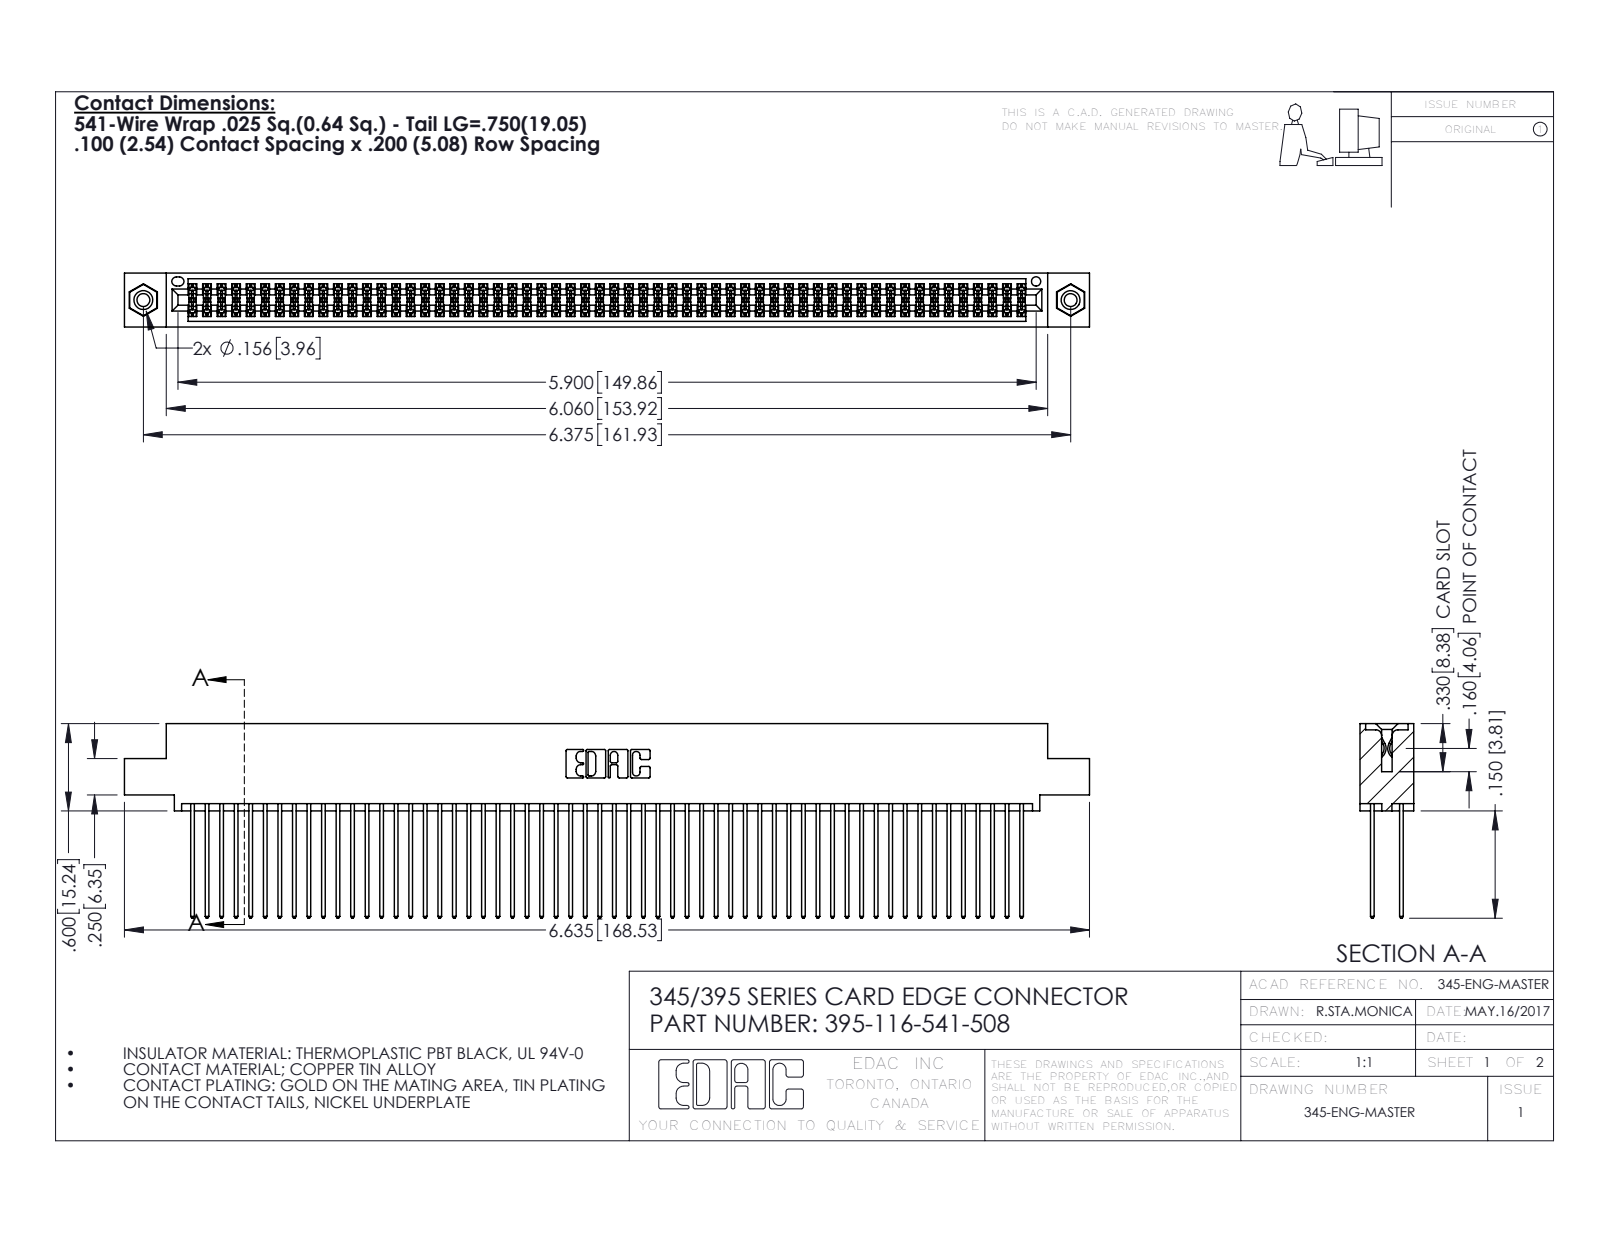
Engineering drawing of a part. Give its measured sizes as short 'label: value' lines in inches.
name: 345-292-001_345-293-141; 345 Part_0.110 Offset - 0.156 Dia-TI; 345-250-001_345-250-003-102; 395-116-541-508
written by: SolidWorks 2016 (CONFIG_CONTROL_DESIGN)
unit: in
bodies: 119 solids, 5990 faces (3944 planar, 2030 cylindrical, 16 other)
size: 6.635 × 1.337 × 0.37
volume: 1.044 in³; area: 44.68 in²
holes: 2× ⌀0.089, 2× ⌀0.125, 2× ⌀0.156, 1× ⌀0.064
bosses: 2× ⌀0.155
rounds: 174× R0.006, 116× R0.01, 22× R0.01, 6× R0.007, 6× R0.031, 3× R0.026, 2× R0.014, 2× R0.019
face distances: 0.072, 0.298, 0.2, 0.098, 0.272, 0.025, 0.225, 0.37, 0.175, 0.149
hole spacings: 0.27, 6.139, 6.375
